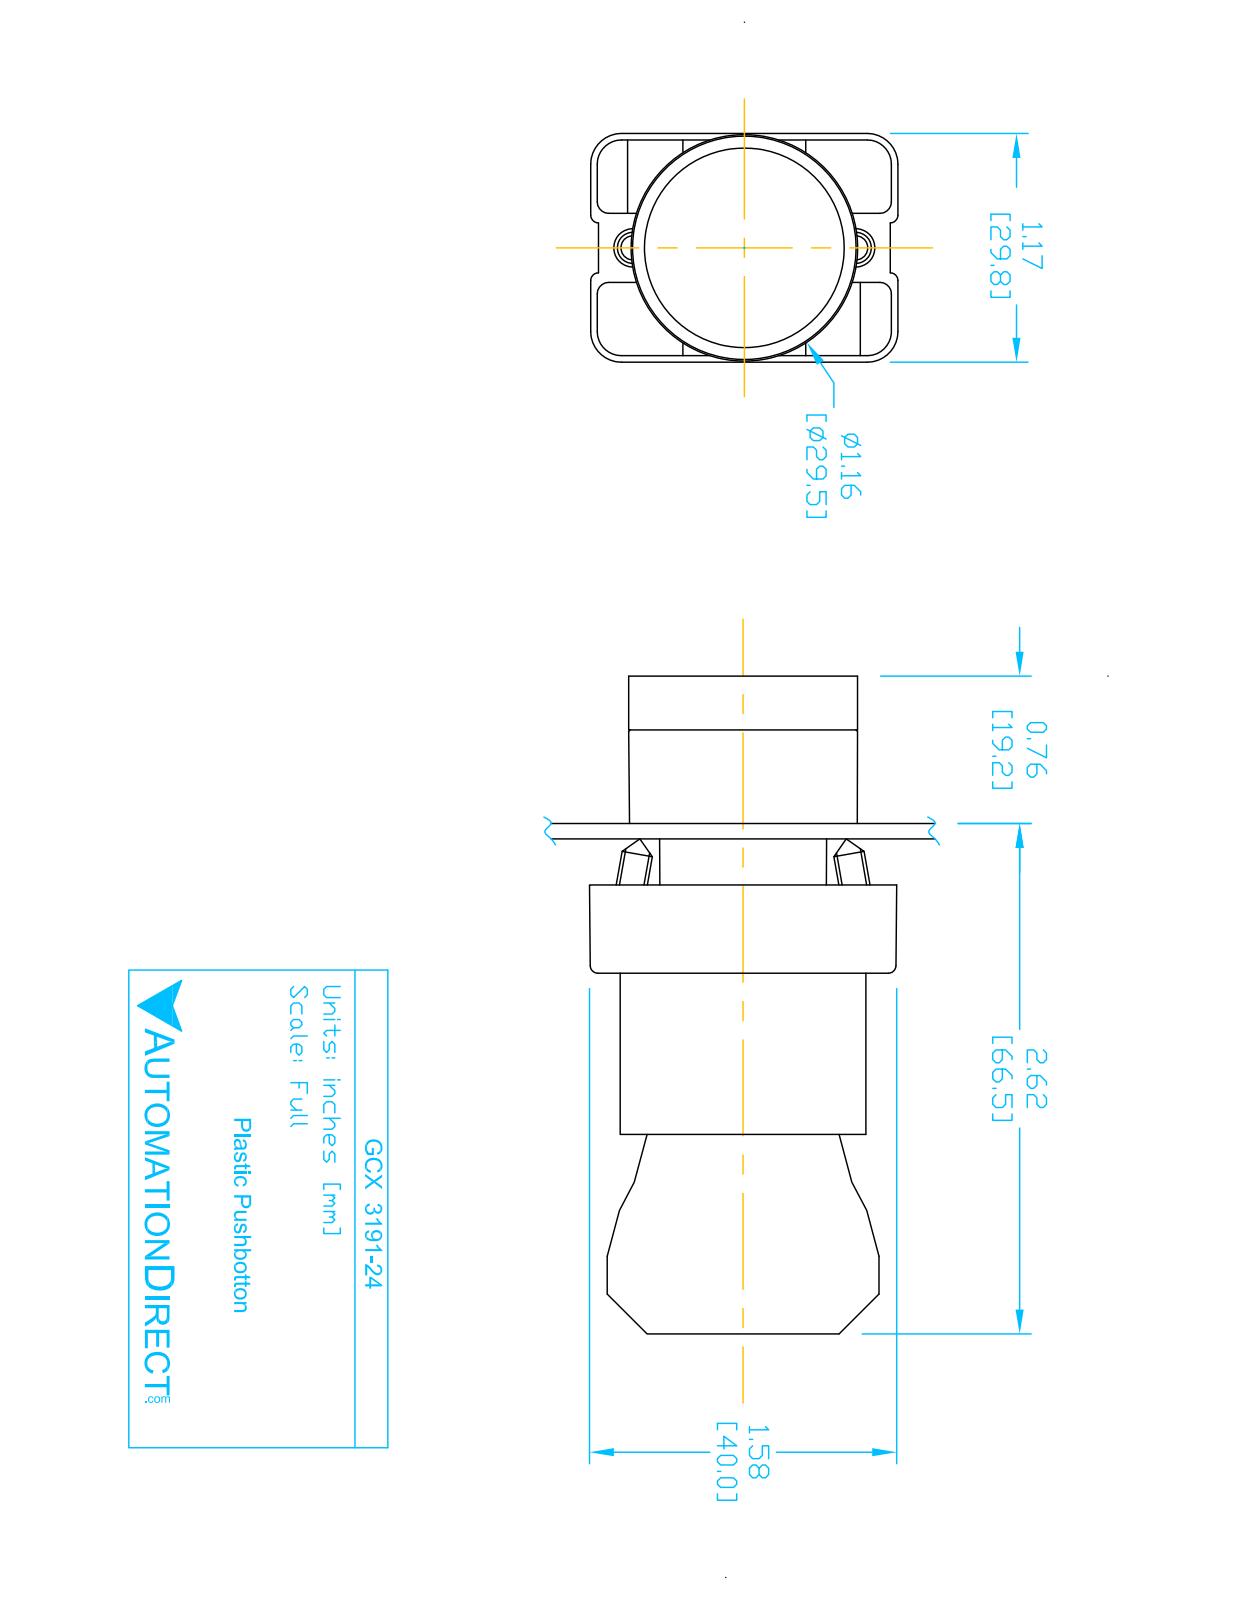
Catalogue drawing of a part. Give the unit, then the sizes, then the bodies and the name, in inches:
Units: inches
Overall size (bounding box): 3.319 × 1.581 × 1.177
Round holes (diameter × count): ⌀0.079 ×2, ⌀0.124 ×2, ⌀0.13 ×2, ⌀0.087 ×1, ⌀0.197 ×1, ⌀0.469 ×1, ⌀0.878 ×1, ⌀0.888 ×1, ⌀1.024 ×1
Round bosses / shafts (diameter × count): ⌀0.157 ×4, ⌀1.175 ×1, ⌀1.004 ×1, ⌀0.945 ×1, ⌀0.856 ×1, ⌀0.78 ×1, ⌀0.504 ×1
Partial cylindrical surfaces — rounded edges, fillets, slot ends (radius × count): R0.059 ×24, R0.041 ×12, R0.124 ×12, R0.157 ×12, R0.039 ×8, R0.128 ×2, R0.02 ×1, R0.063 ×1
Main face-to-face distances: 0.827, 0.579, 2.02, 1.193, 1.171, 0.276, 2.295, 1.469, 0.031, 0.033
Hole centre spacings: 0.236, 0.544, 0.472, 0.49
Volume: 2.794 in³ · Surface area: 38.77 in²
Bodies: 8 solids, 431 faces (252 planar, 148 cylindrical, 31 other)
Part name (STEP PRODUCT): ECX1050; GCX3191 OPERATOR; GCX3191-24; ECX3029-2 (+1 more)
STEP written by: SolidWorks 2016 (AUTOMOTIVE_DESIGN)
